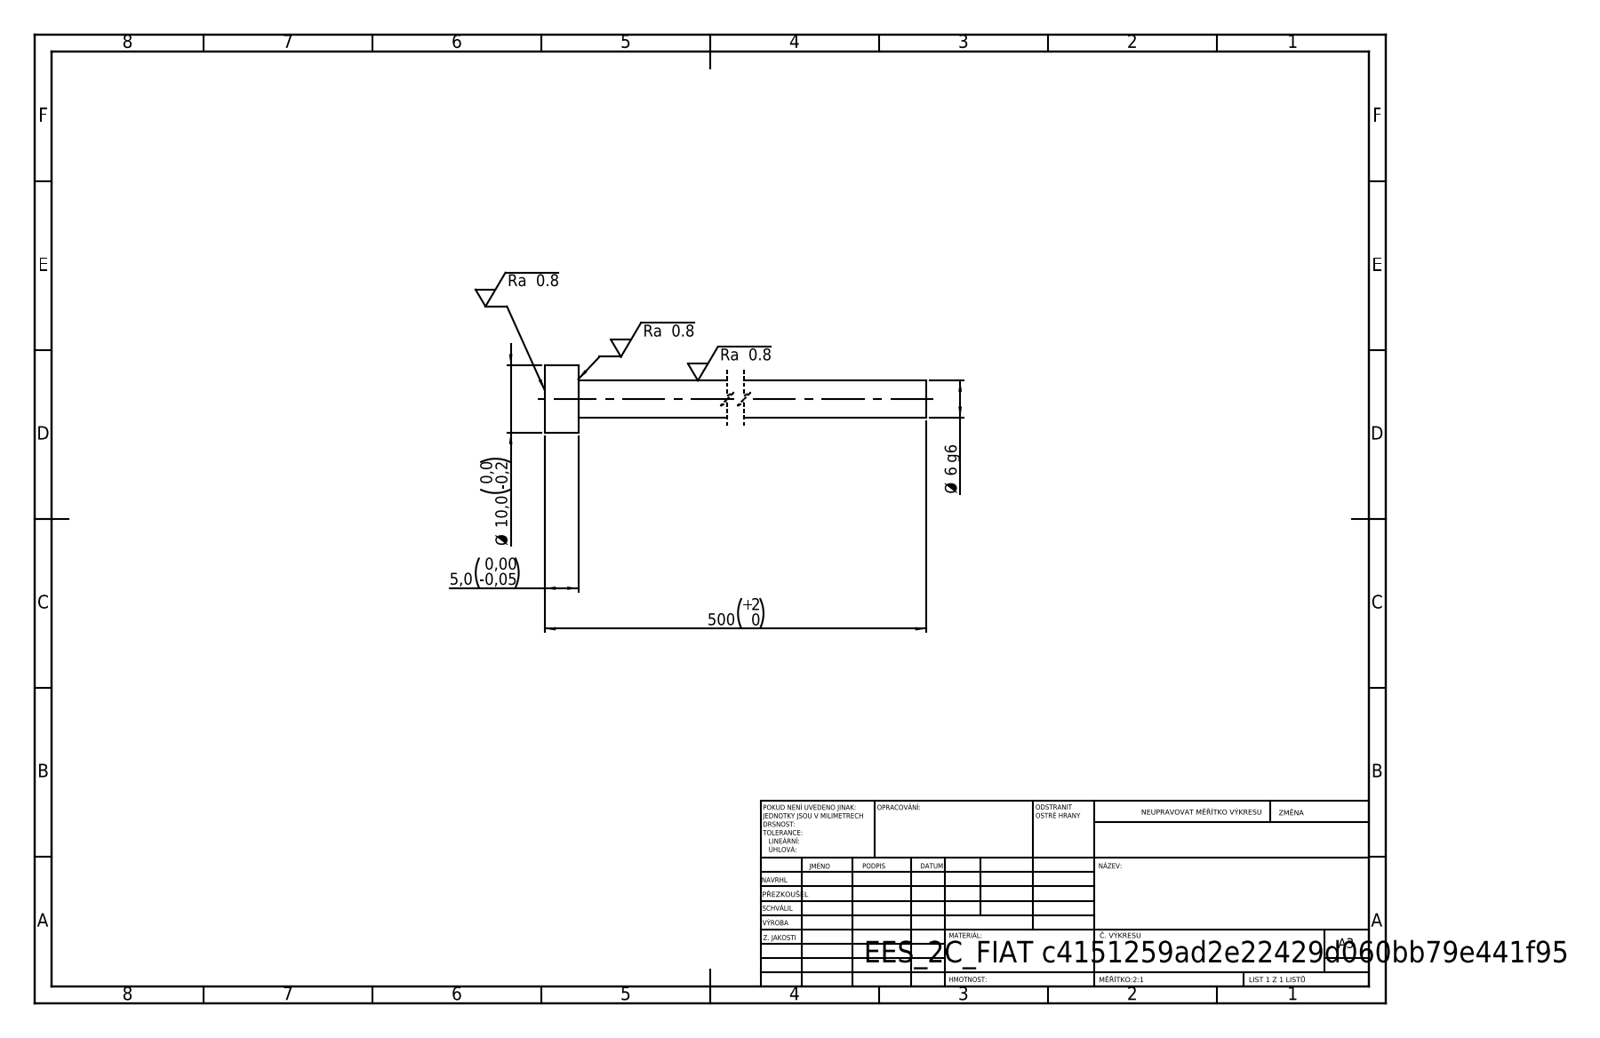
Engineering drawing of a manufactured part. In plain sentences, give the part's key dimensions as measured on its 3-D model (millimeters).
Its 3-D file was written by "SolidWorks 2019 (CONFIG_CONTROL_DESIGN)". It is 1 solid with 7 faces: 3 planar, 4 cylindrical and 0 other. Overall it measures 500 by 10 by 10 millimeters. Its volume is 12 153 cubic millimeters and its surface area 8 867 square millimeters. Round bosses or shafts: 1 of diameter 10, 1 of diameter 5.5. The main face-to-face distances are 5, 500, 495.
